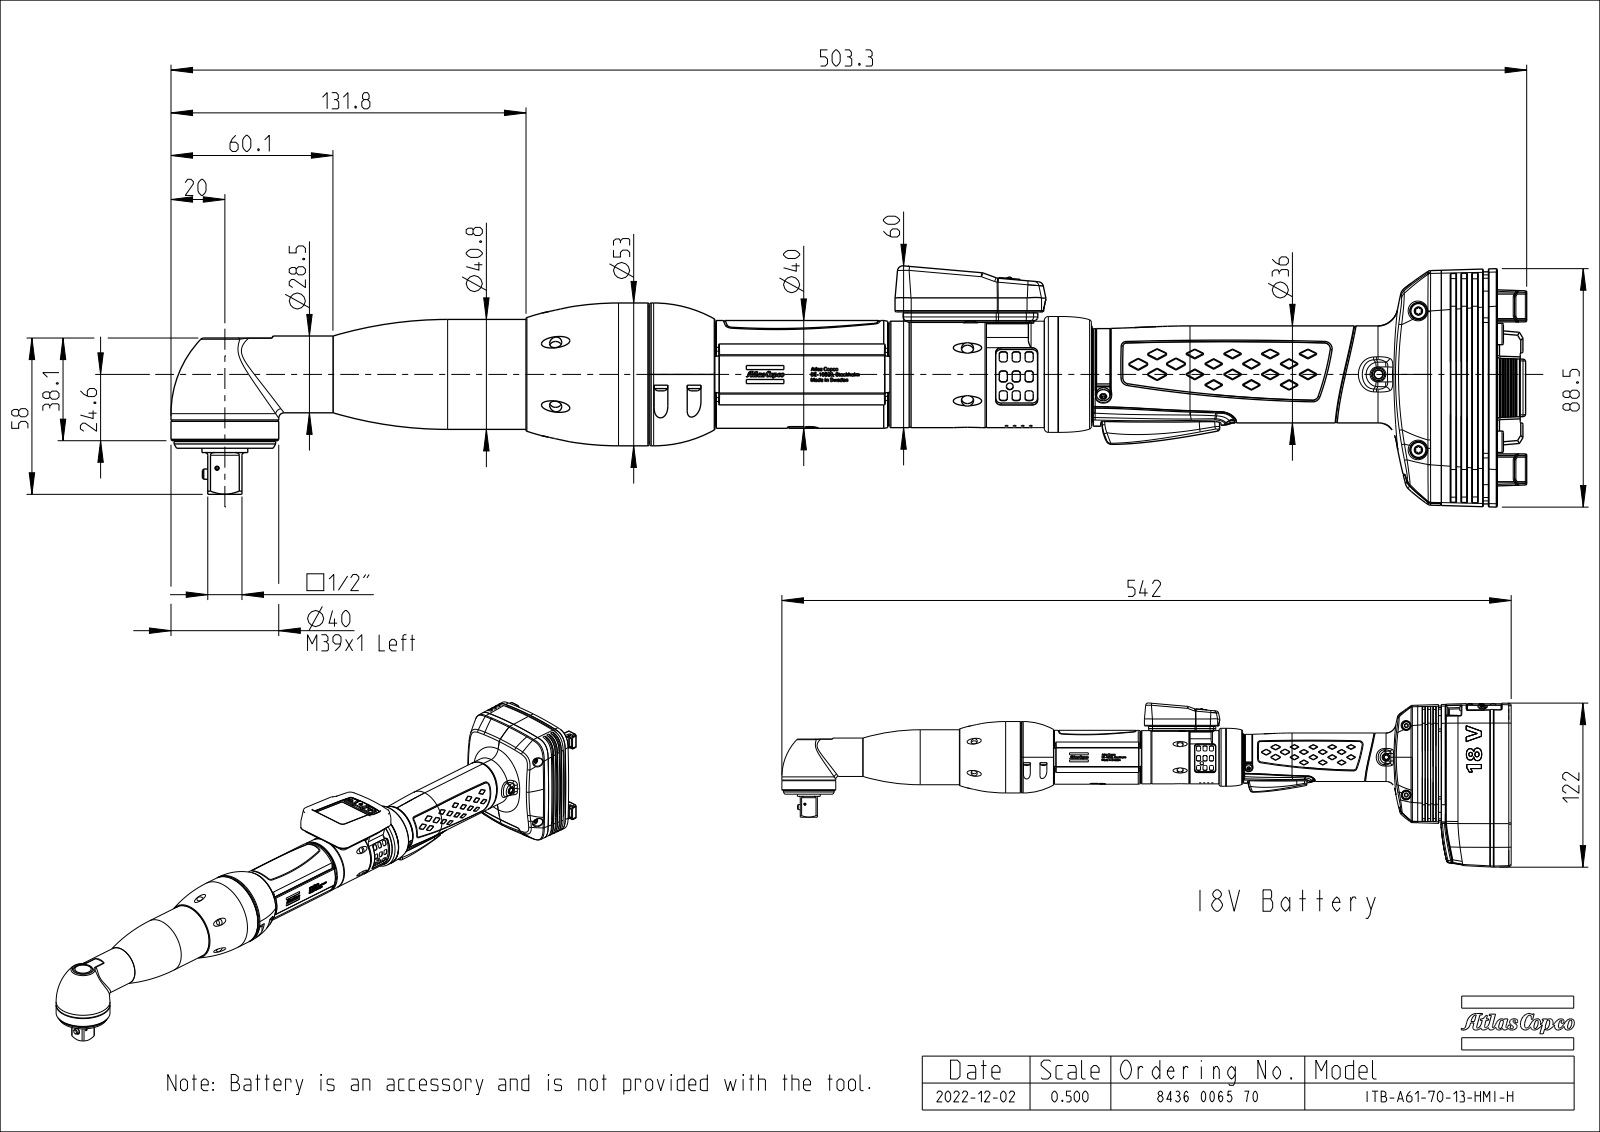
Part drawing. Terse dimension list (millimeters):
name: EXT_COMP_SW0016
written by: CREO PARAMETRIC BY PTC INC, 2020281 (CONFIG_CONTROL_DESIGN)
unit: mm
bodies: 11 solids, 11520 faces (4260 planar, 2547 cylindrical, 4713 other)
size: 503.8 × 89.5 × 74.5
volume: 622 900 mm³; area: 190 400 mm²
holes: 12× ⌀1, 11× ⌀4.5, 9× ⌀2.5, 9× ⌀3.2, 4× ⌀2.2, 4× ⌀3, 4× ⌀3.3, 4× ⌀4.3, 4× ⌀5.8, 4× ⌀6.5, 3× ⌀1.6, 3× ⌀4
bosses: 4× ⌀5, 3× ⌀3.5, 2× ⌀40, 2× ⌀6.2, 2× ⌀5.6, 2× ⌀5.5, 2× ⌀4, 2× ⌀3
rounds: 443× R0.3, 244× R0.5, 229× R0.2, 126× R1, 106× R2, 36× R0.1, 30× R1.5, 29× R3
face distances: 11.2, 5.1, 2, 3, 20.2, 13.5, 9, 34.2, 23.1, 0.4
hole spacings: 3, 6, 13, 18.4, 19.1, 55.5, 58.3, 78.2
